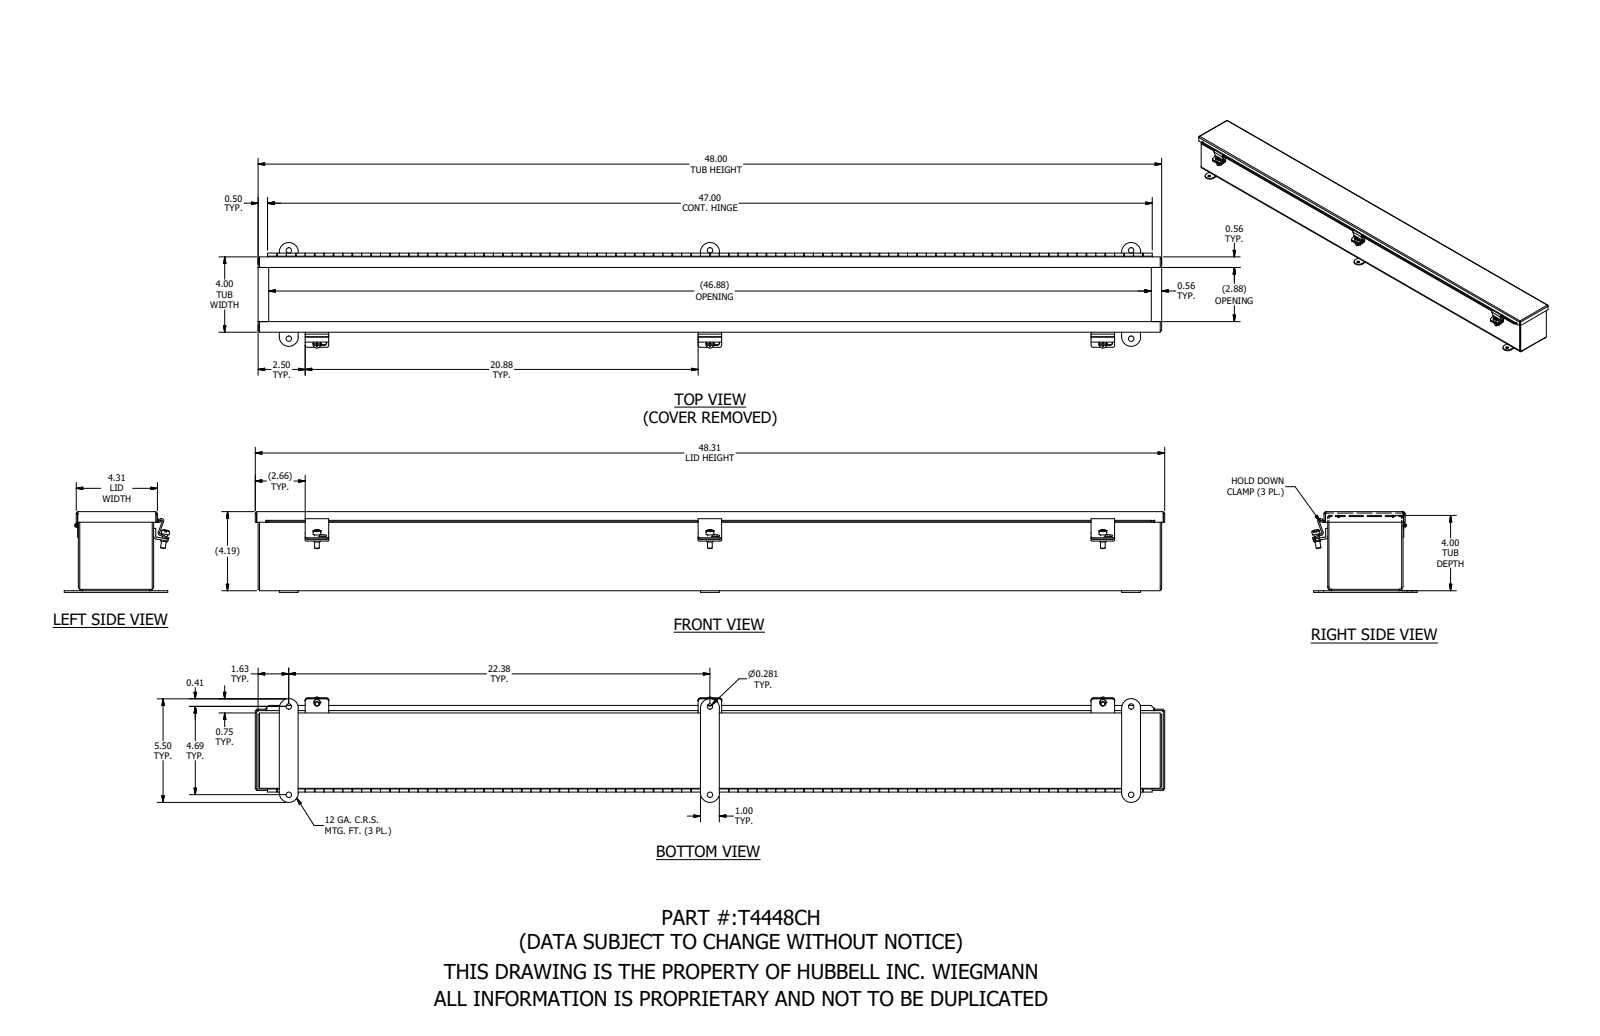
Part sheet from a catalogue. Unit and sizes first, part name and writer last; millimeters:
Units: millimetres
Overall size (bounding box): 1227.2 × 142.1 × 108.8
Round holes (diameter × count): ⌀7.1 ×6, ⌀5 ×3, ⌀2.9 ×1
Round bosses / shafts (diameter × count): ⌀10.4 ×3, ⌀8.7 ×3, ⌀6.4 ×3, ⌀5.1 ×1, ⌀2.5 ×1
Partial cylindrical surfaces — rounded edges, fillets, slot ends (radius × count): R3.2 ×12, R0.8 ×9, R2.7 ×9, R3.4 ×6, R12.7 ×6, R1.6 ×3, R3.2 ×3, R4 ×2
Main face-to-face distances: 1.9, 99.7, 104.5, 101.6, 97.8, 106.4, 102.6, 4.8, 102.7, 2.9
Hole centre spacings: 119, 568.3, 568.3, 580.7, 580.7, 1136.7, 1142.9, 530.2
Volume: 1 187 000 mm³ · Surface area: 1 320 000 mm²
Bodies: 19 solids, 993 faces (486 planar, 484 cylindrical, 23 other)
Part name (STEP PRODUCT): T4448CH
STEP written by: SolidWorks 2021 (AUTOMOTIVE_DESIGN)
